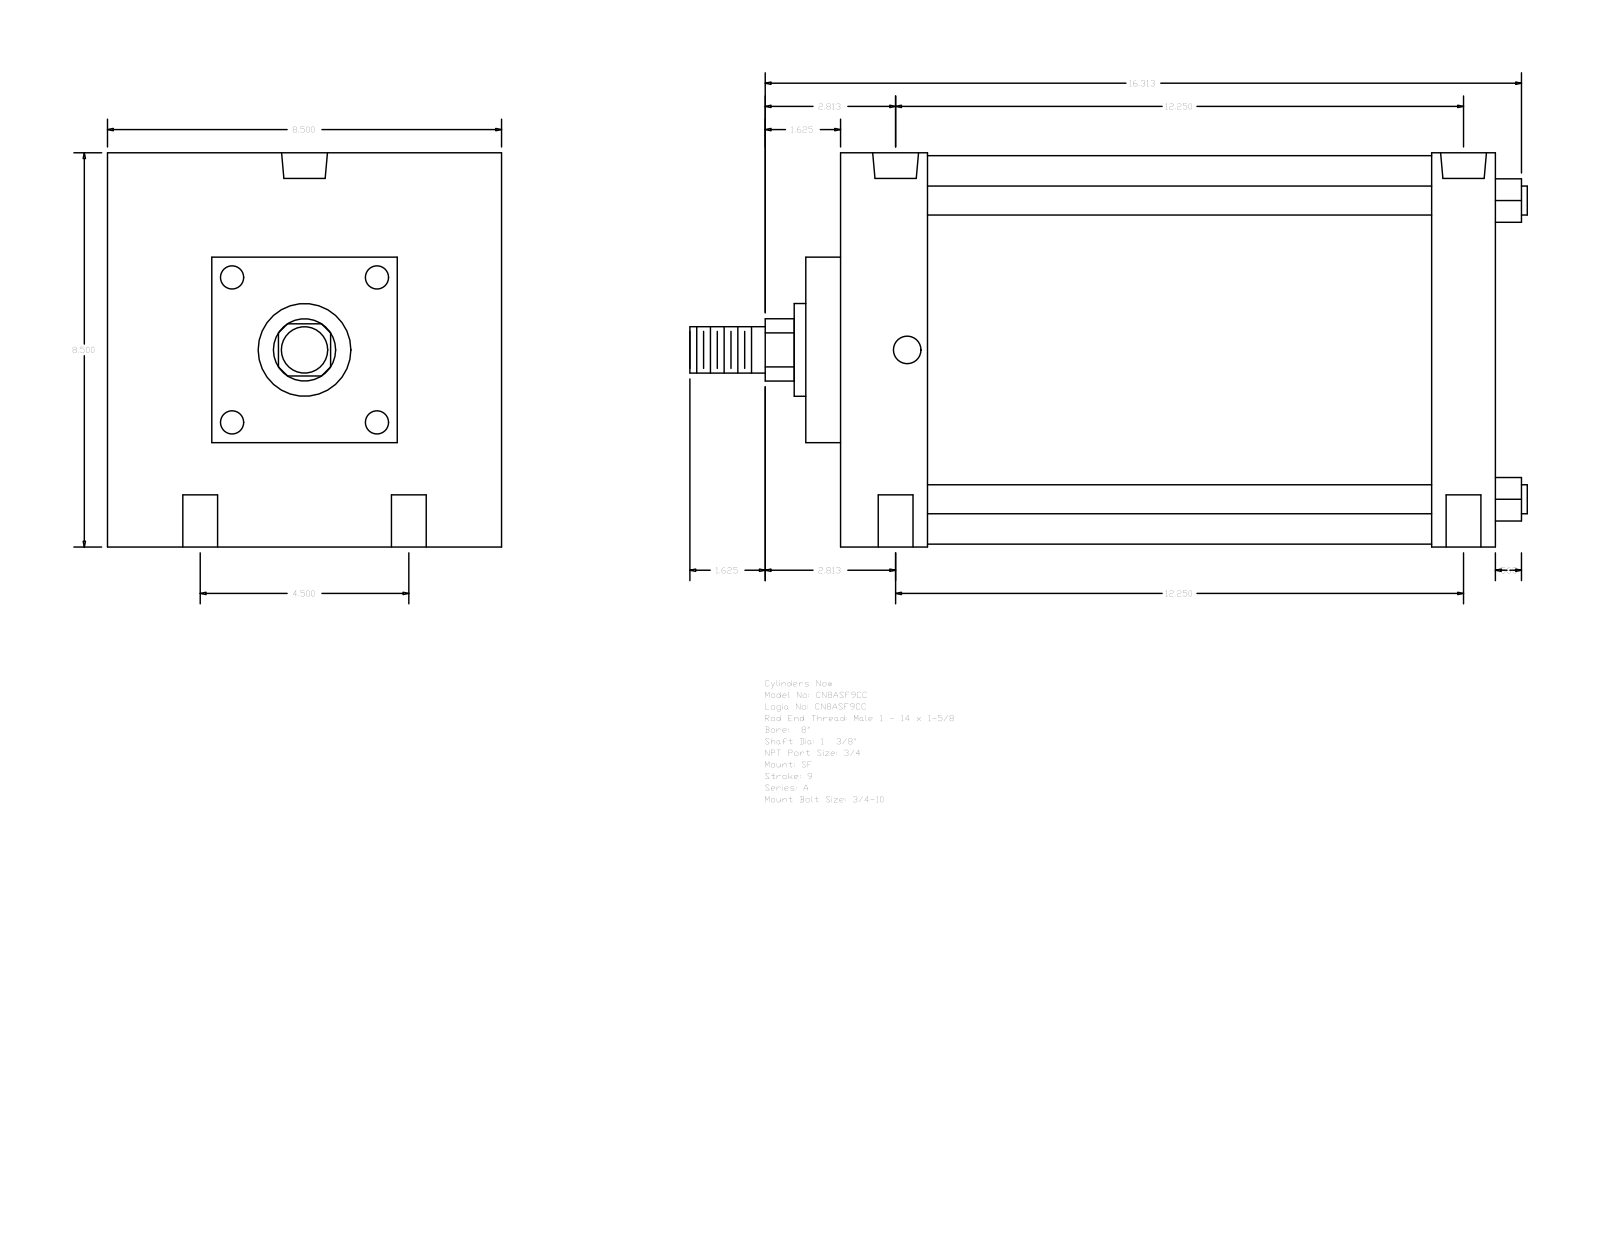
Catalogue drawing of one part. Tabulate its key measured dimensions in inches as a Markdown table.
| quantity | value |
| --- | --- |
| part name | A_SF__0800_1.375 |
| STEP written by | GSSL Pune (CONFIG_CONTROL_DESIGN) |
| units | inches |
| bodies | 0 solids, 93 faces (67 planar, 26 cylindrical, 0 other) |
| overall size | 18.063 × 8.5 × 8.5 |
| round holes (diameter × count) | 0.75 × 4, 0.594 × 2, 0.989 × 2 |
| round bosses / shafts (diameter × count) | 0.625 × 4, 8.375 × 1, 2 × 1, 1.375 × 1, 1 × 1 |
| partial cylindrical surfaces (radius × count) | 0.672 × 1 |
| main face-to-face distances | 14.125, 8.5, 1.875, 12.75, 10.875, 12.25, 1.375, 0.75, 2.625, 13.5 |
| hole center spacings | 2.25, 12.455, 12.25, 4.5, 13.05, 11.75 |
